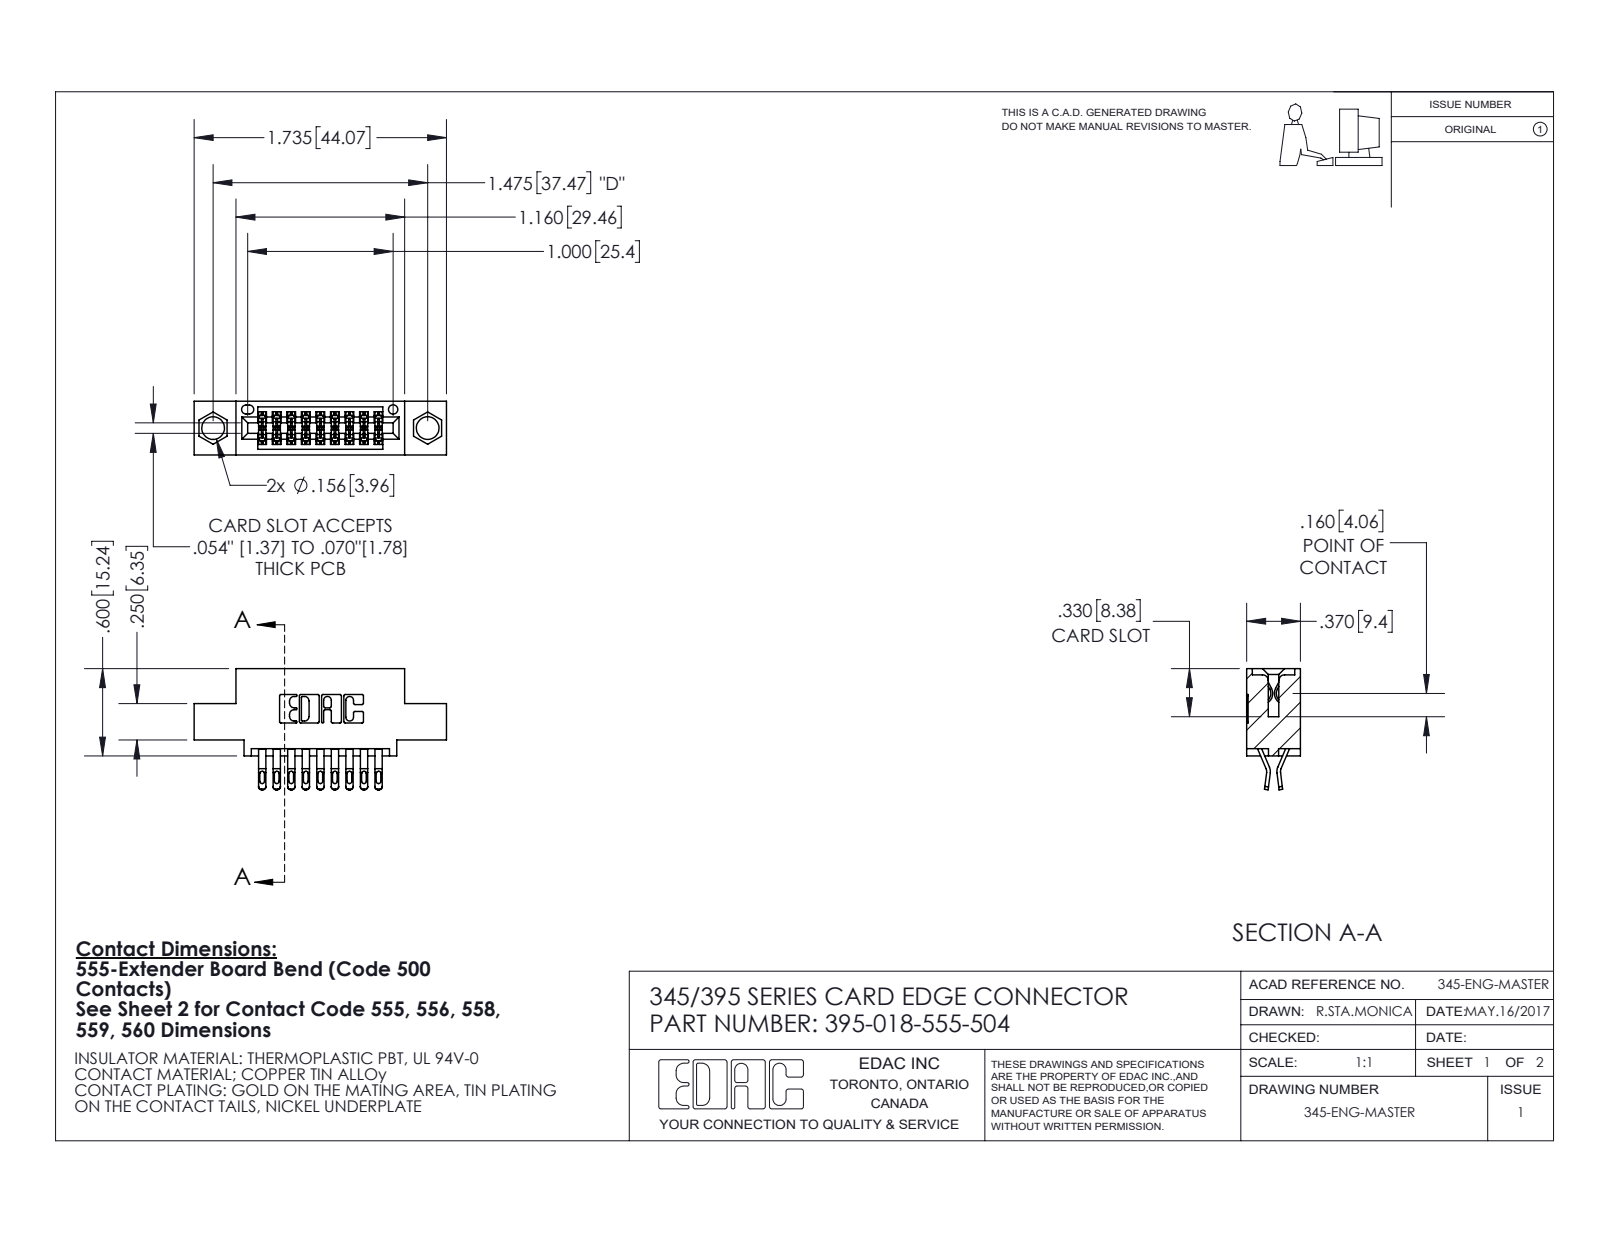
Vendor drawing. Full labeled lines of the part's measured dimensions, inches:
Part name (STEP PRODUCT): 345 Part_0.110 Offset - 0.156 Dia-TI; 345-292-001_555 Tail; 395-018-555-504
STEP written by: SolidWorks 2020 (CONFIG_CONTROL_DESIGN)
Units: inches
Bodies: 19 solids, 1152 faces (656 planar, 496 cylindrical, 0 other)
Overall size (bounding box): 1.735 × 0.832 × 0.37
Volume: 0.235 in³ · Surface area: 8.02 in²
Round holes (diameter × count): ⌀0.156 ×2, ⌀0.064 ×1
Partial cylindrical surfaces — rounded edges, fillets, slot ends (radius × count): R0.016 ×45, R0.006 ×36, R0.02 ×36, R0.01 ×22, R0.007 ×6, R0.031 ×6, R0.026 ×3, R0.01 ×2
Main face-to-face distances: 0.2, 0.298, 0.072, 0.37, 0.1, 0.025, 0.098, 0.272, 0.225, 0.6
Hole centre spacings: 0.27, 1.244, 1.475
